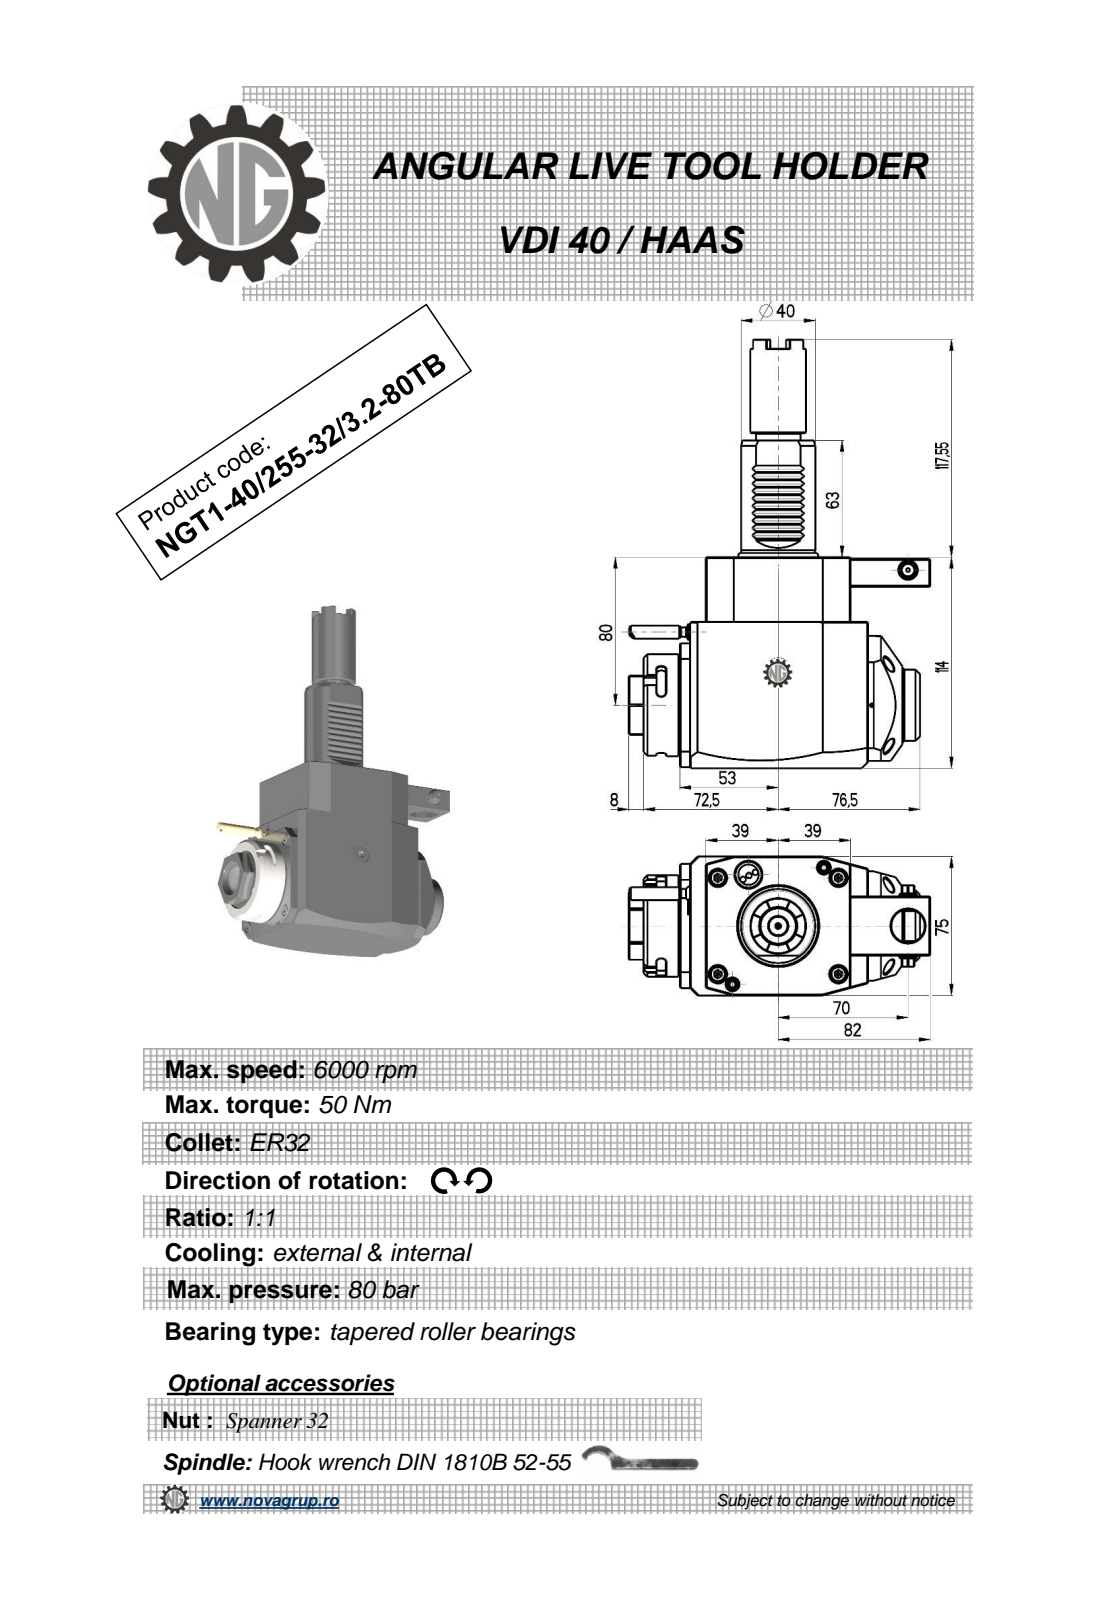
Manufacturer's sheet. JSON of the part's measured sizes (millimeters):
{"part_name": "NGT1_40_255_32_3_2_80TB", "step_written_by": "PRO/ENGINEER BY PARAMETRIC TECHNOLOGY CORPORATION, 2010280 (CONFIG_CONTROL_DESIGN)", "units": "millimeters", "bodies": {"solids": 1, "faces": 397, "planar": 219, "cylindrical": 88, "other": 90}, "overall_size": [231.55, 162.5, 75], "volume_mm3": 1015000, "surface_area_mm2": 79616, "round_holes": [[2, 1], [2.5, 1], [3, 1], [9.5, 1], [18, 1], [20, 1], [23, 1]], "round_bosses_or_shafts": [[8.96, 2], [55, 1], [48, 1], [40, 1], [38.5, 1], [30, 1], [24, 1], [10, 1]], "partial_cylinders_radius": [[0.3, 10], [2.5, 6], [180, 2], [0.5, 1], [3.85, 1], [4.25, 1], [24.5, 1], [37.5, 1]], "face_to_face_distances": [75, 114, 14, 33.5, 79, 92, 78, 21.5, 98, 19.5], "hole_center_spacings": [37.35, 43.2, 70, 72.5]}
